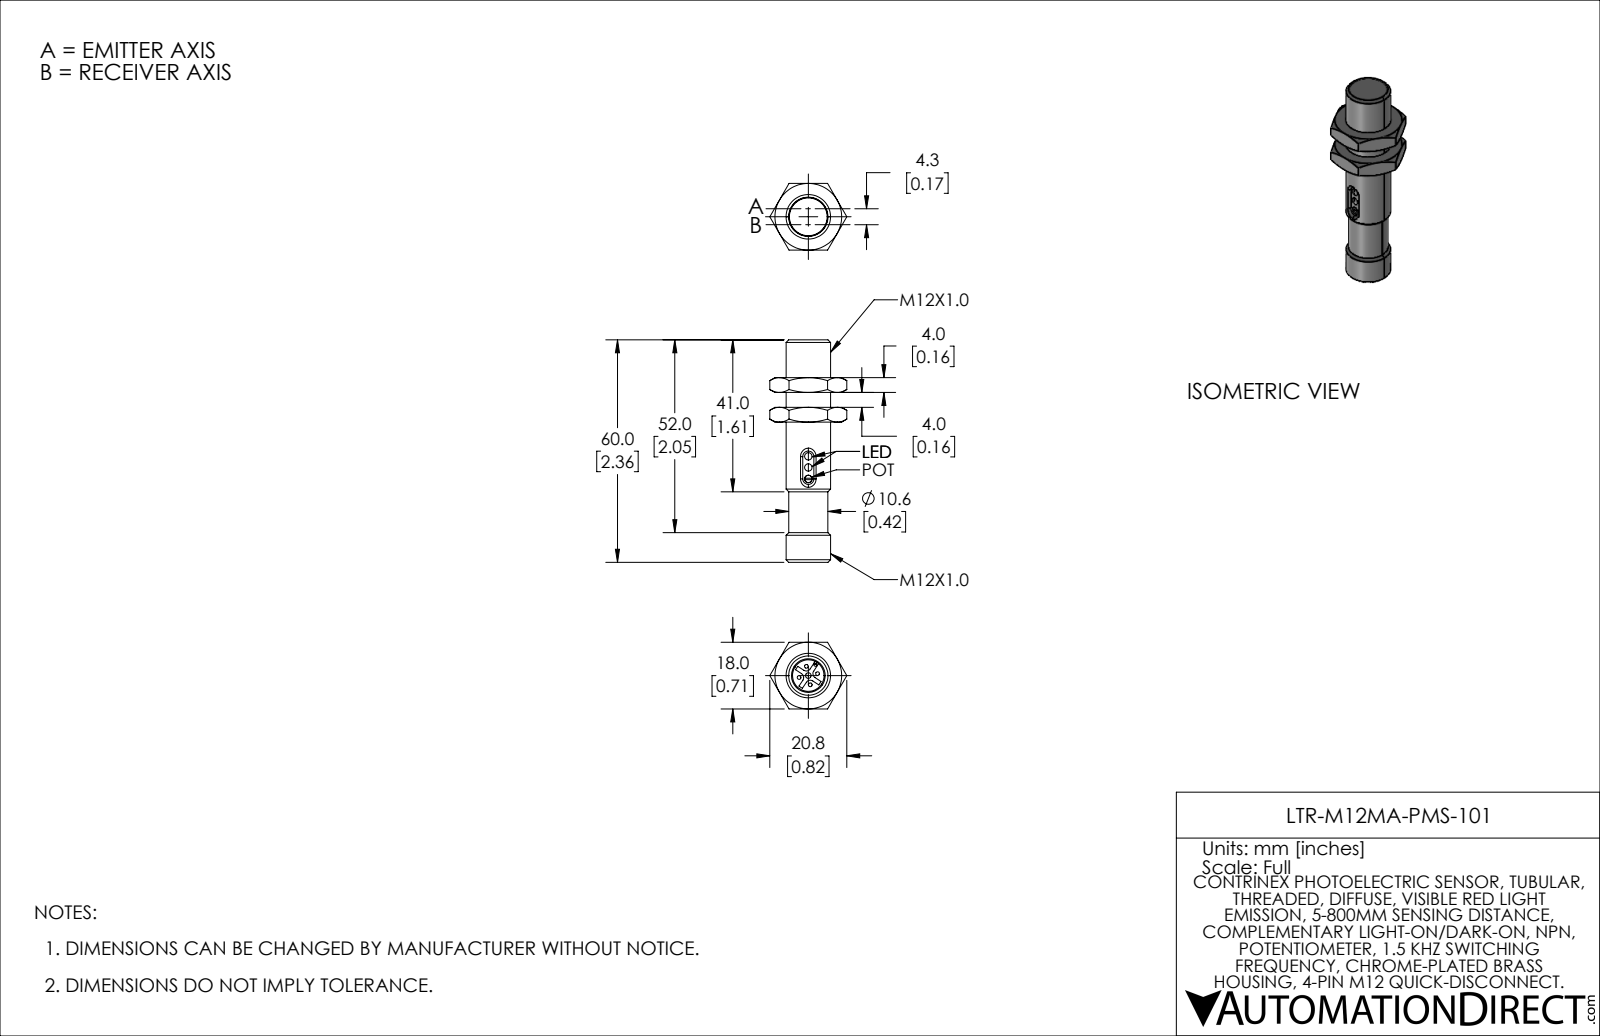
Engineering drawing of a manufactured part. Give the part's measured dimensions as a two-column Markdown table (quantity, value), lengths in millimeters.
| quantity | value |
| --- | --- |
| part name | LTR-M12MA-PMS-101 |
| STEP written by | SolidWorks 2021 (AUTOMOTIVE_DESIGN) |
| units | millimeters |
| bodies | 4 solids, 167 faces (46 planar, 51 cylindrical, 70 other) |
| overall size | 60 × 20.79 × 18 |
| volume | 7 472 mm³ |
| surface area | 4 224 mm² |
| round holes (diameter × count) | 1.5 × 1, 2 × 1, 8.5 × 1, 10.2 × 1, 12 × 1 |
| round bosses / shafts (diameter × count) | 1 × 4, 10.55 × 1 |
| partial cylindrical surfaces (radius × count) | 1.25 × 4, 0.5 × 2, 0.55 × 1, 1 × 1 |
| main face-to-face distances | 4, 18, 8, 12, 10, 14, 22, 51, 41, 37 |
